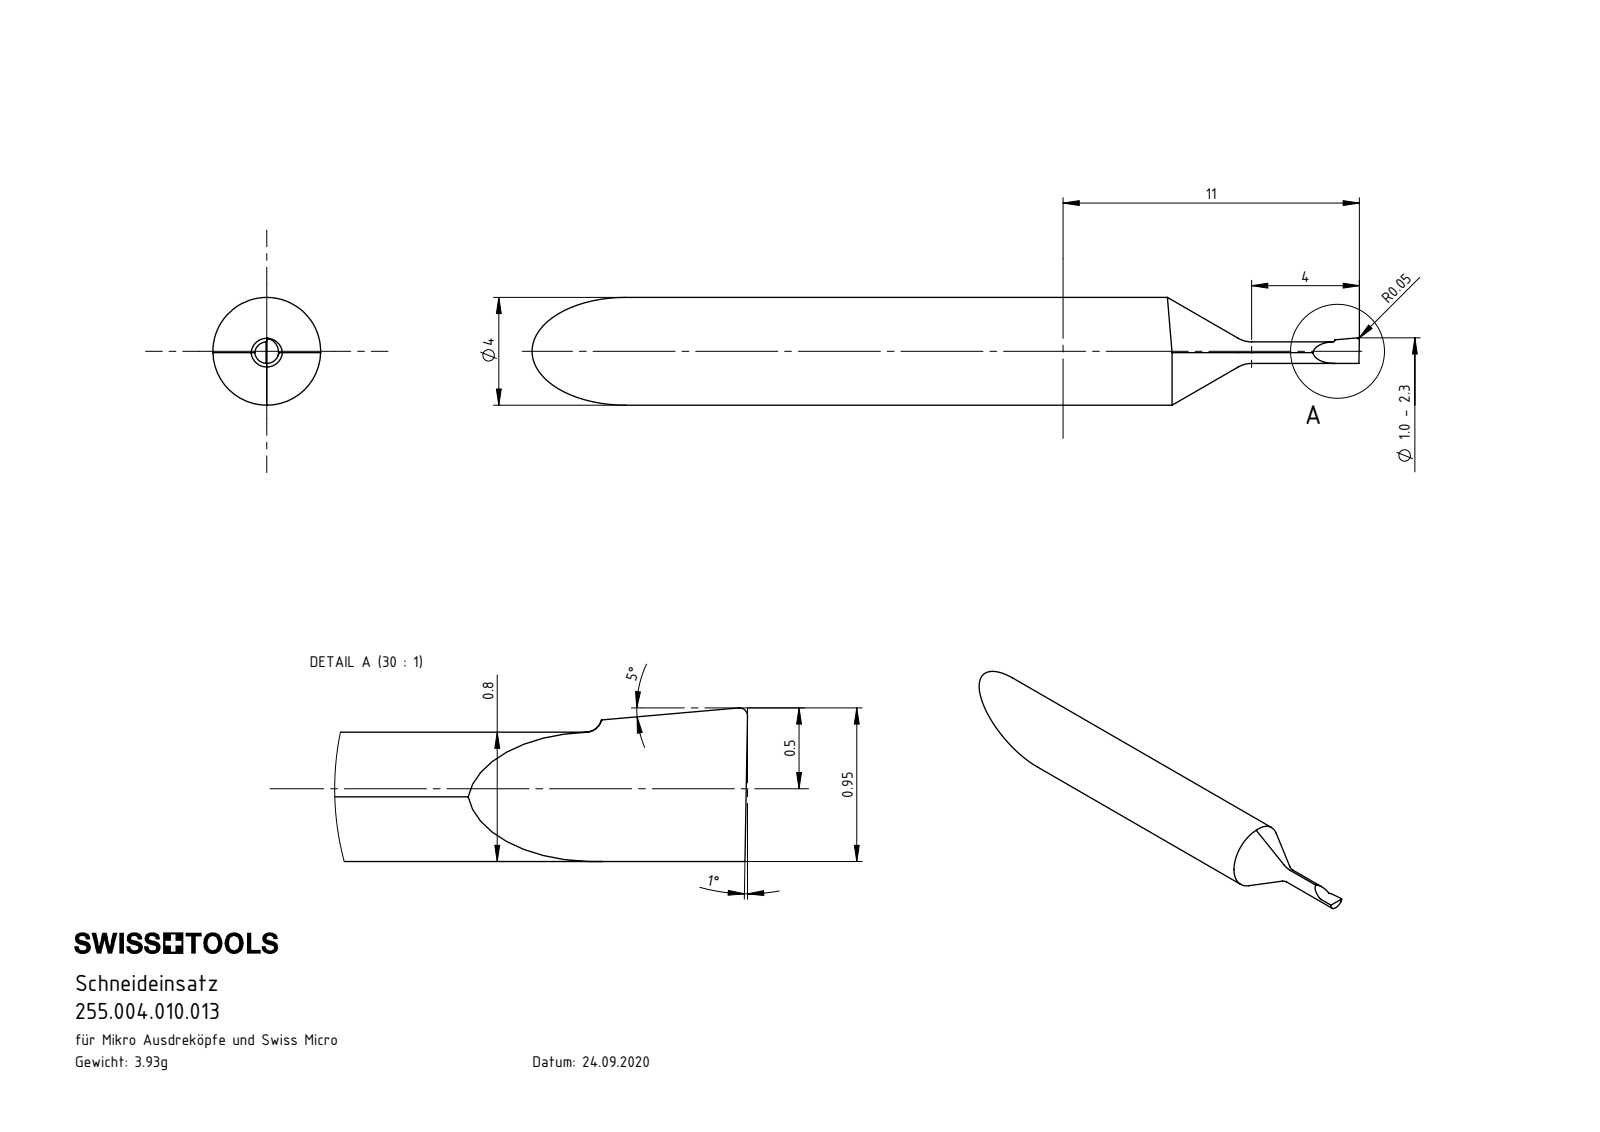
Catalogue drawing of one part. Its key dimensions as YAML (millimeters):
part_name: "A04.0045.04.10.05_YR"
step_written_by: "SolidWorks 2017 (AUTOMOTIVE_DESIGN)"
units: millimeters
bodies: {solids: 1, faces: 26, planar: 5, cylindrical: 7, other: 14}
overall_size: [30.71, 4, 4]
volume: 271
surface_area: 315
round_bosses_or_shafts:
  - {diameter: 4, count: 1}
partial_cylinders:
  - {radius: 0.45, count: 2}
  - {radius: 0.2, count: 1}
face_to_face_distances: [13.15]
